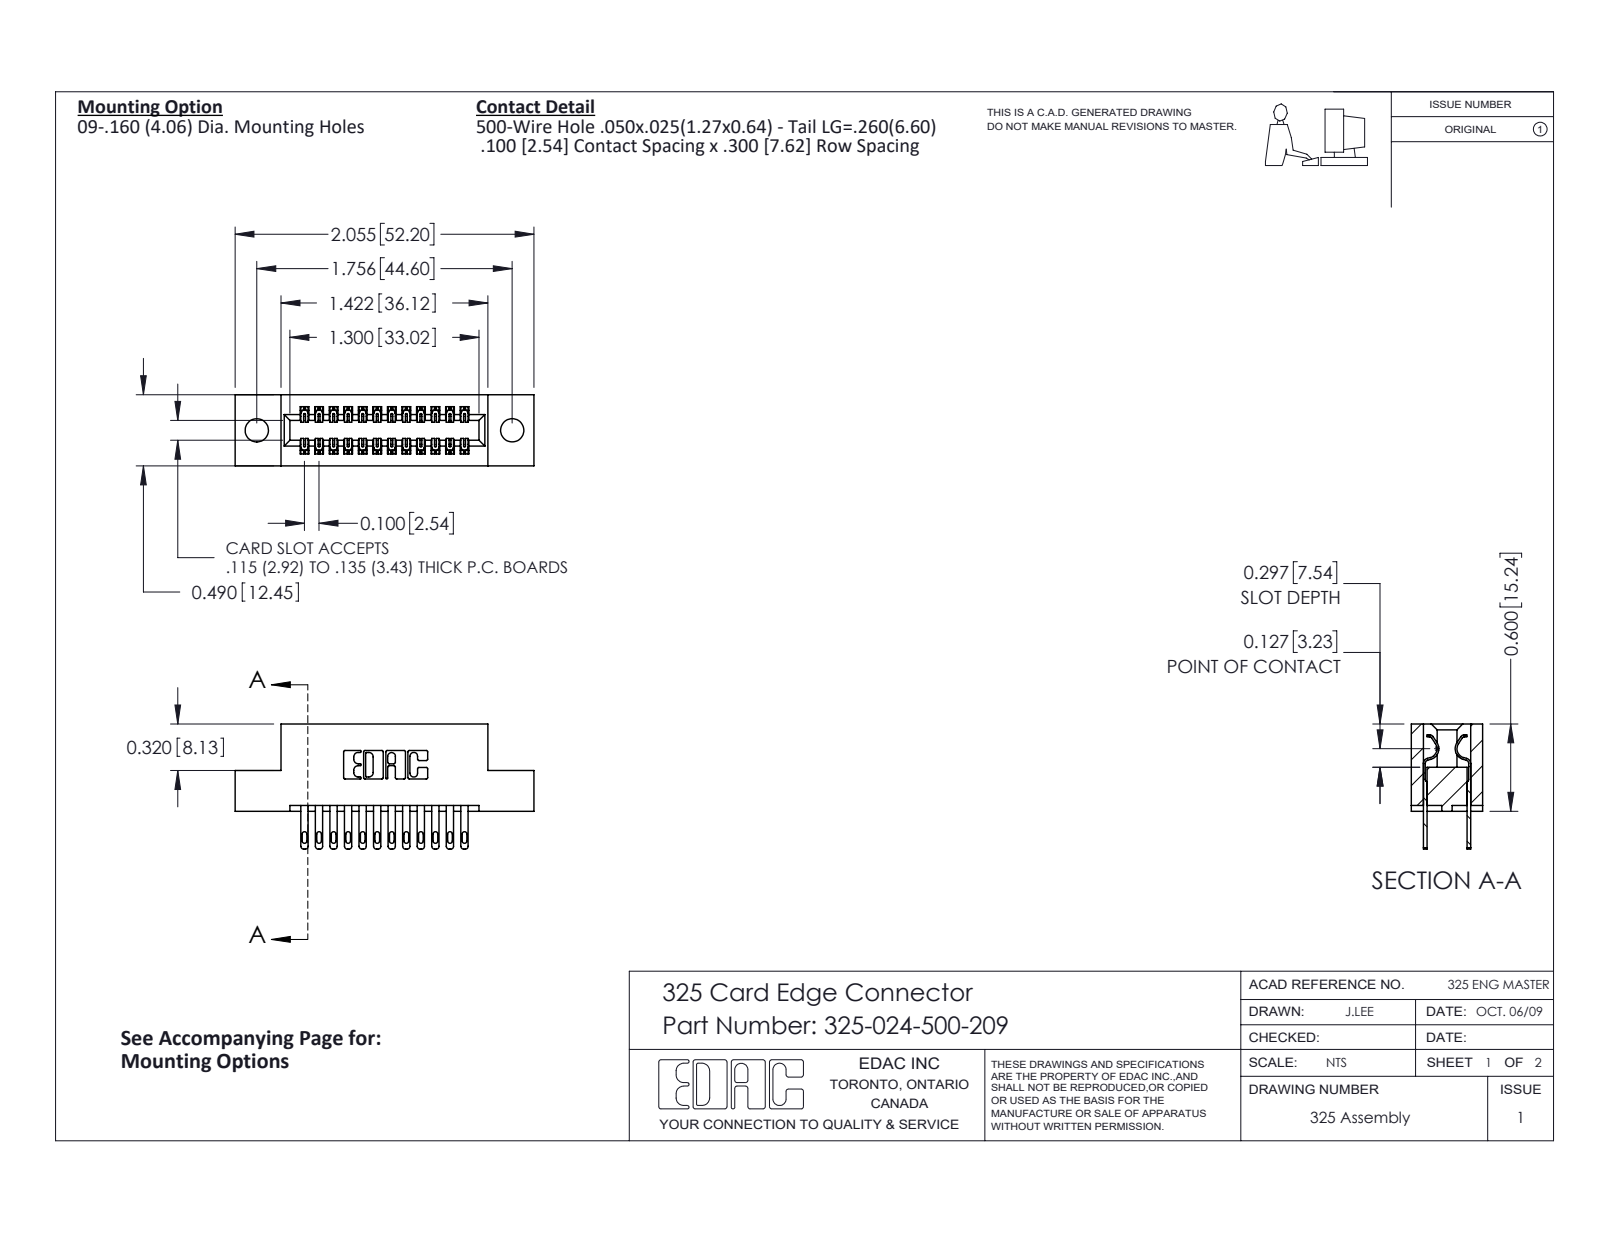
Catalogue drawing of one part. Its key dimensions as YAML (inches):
part_name: "325 Part_.160 TH; 325-024-500-209; 325-292-001_325-293-100"
step_written_by: "SolidWorks 2016 (CONFIG_CONTROL_DESIGN)"
units: inches
bodies: {solids: 25, faces: 1266, planar: 790, cylindrical: 476, other: 0}
overall_size: [2.055, 0.86, 0.49]
volume: 0.385
surface_area: 11
round_holes:
  - {diameter: 0.16, count: 2}
partial_cylinders:
  - {radius: 0.006, count: 36}
  - {radius: 0.016, count: 24}
  - {radius: 0.02, count: 24}
  - {radius: 0.01, count: 22}
  - {radius: 0.007, count: 6}
  - {radius: 0.031, count: 6}
  - {radius: 0.026, count: 3}
  - {radius: 0.014, count: 2}
face_to_face_distances: [0.083, 0.407, 0.3, 0.49, 0.107, 0.383, 0.025, 0.04, 0.1, 0.325]
hole_center_spacings: [1.756]
